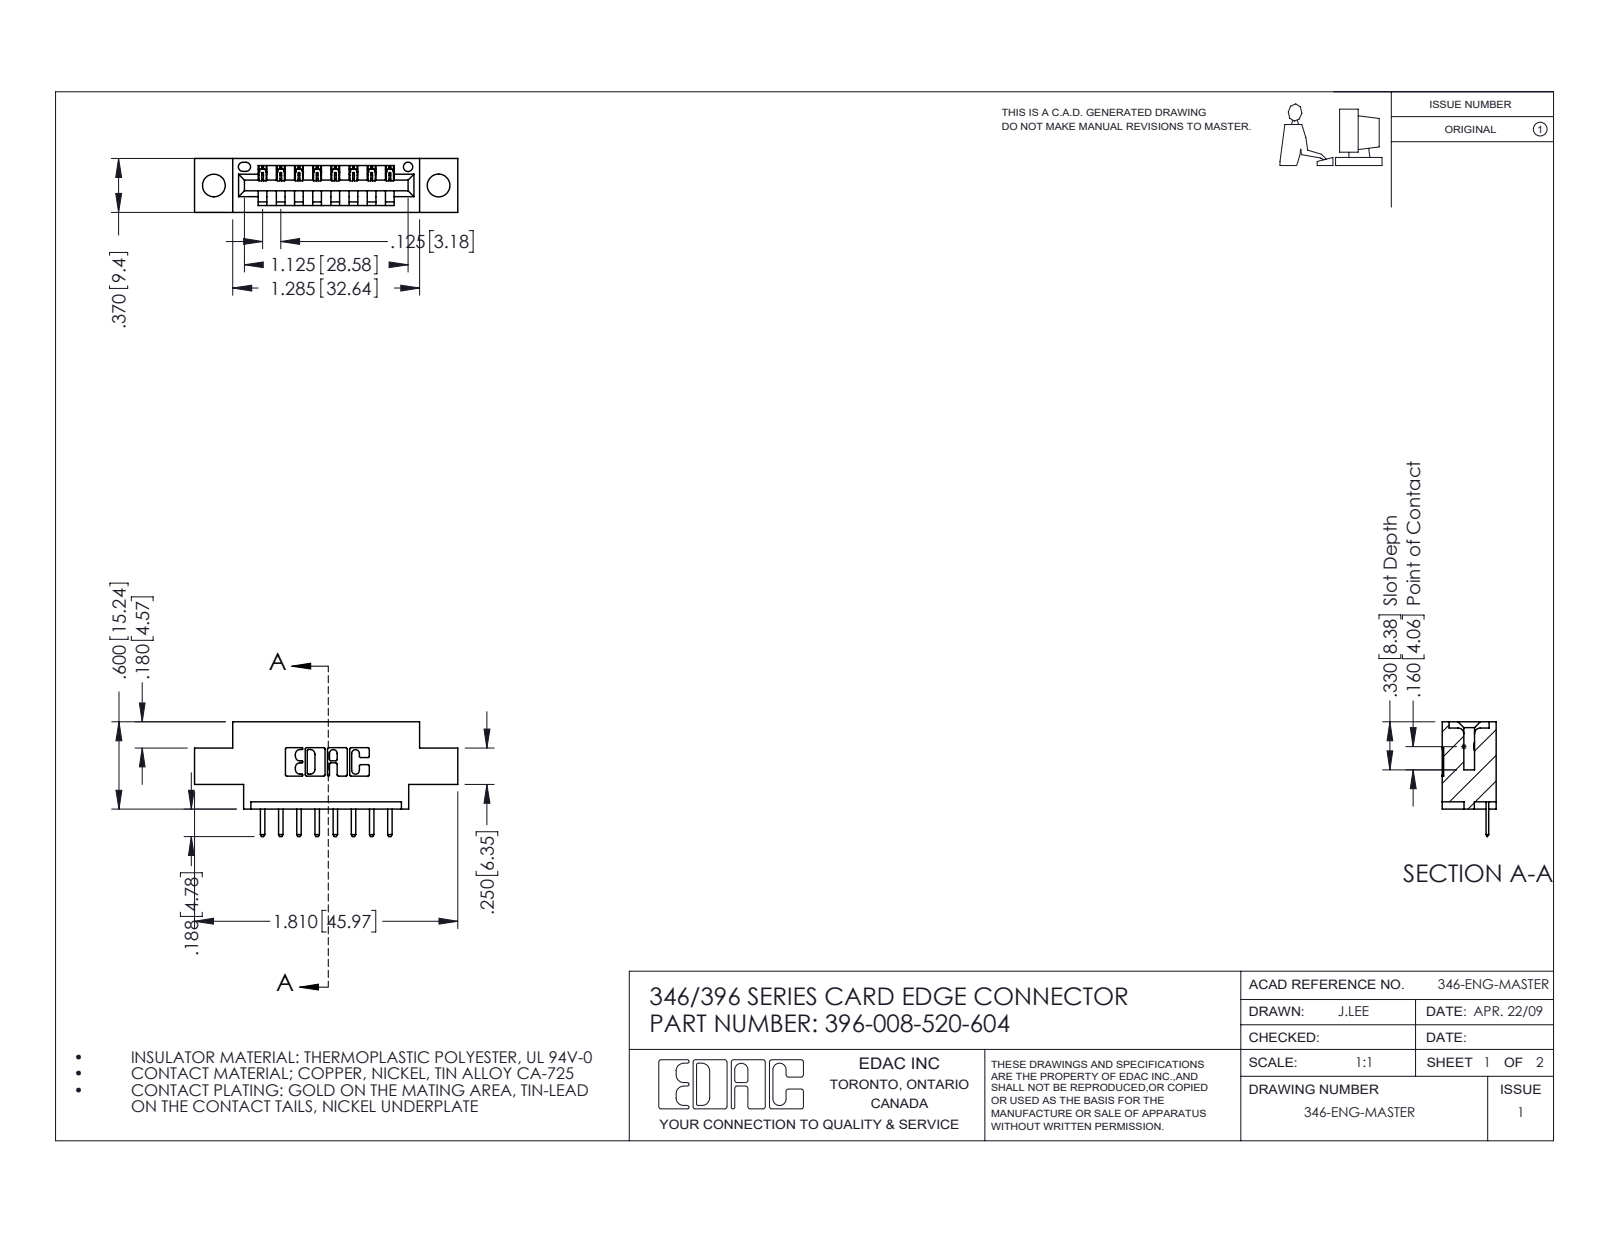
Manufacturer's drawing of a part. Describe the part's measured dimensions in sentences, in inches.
The part is named "346 Part_0.170 Offset - 0.156 Dia-TH; 396-008-520-604; 345-292-001_345-293-120". Its 3-D file was written by "SolidWorks 2016 (CONFIG_CONTROL_DESIGN)". It is 9 solids with 622 faces: 416 planar, 206 cylindrical and 0 other. Overall it measures 1.81 by 0.788 by 0.37 inches. Its volume is 0.238 cubic inches and its surface area 6.816 square inches. Round holes: 2 of diameter 0.156, 1 of diameter 0.064. Partial cylindrical surfaces (rounded edges, fillets, slot ends): 22 of radius 0.01, 18 of radius 0.01, 16 of radius 0.006, 6 of radius 0.007, 6 of radius 0.031, 3 of radius 0.026, 2 of radius 0.031, 2 of radius 0.04. The main face-to-face distances are 0.25, 0.37, 0.048, 0.322, 0.148, 0.222, 0.1, 0.174, 0.5, 0.185. The hole center spacings are 0.246, 1.341, 1.545.
